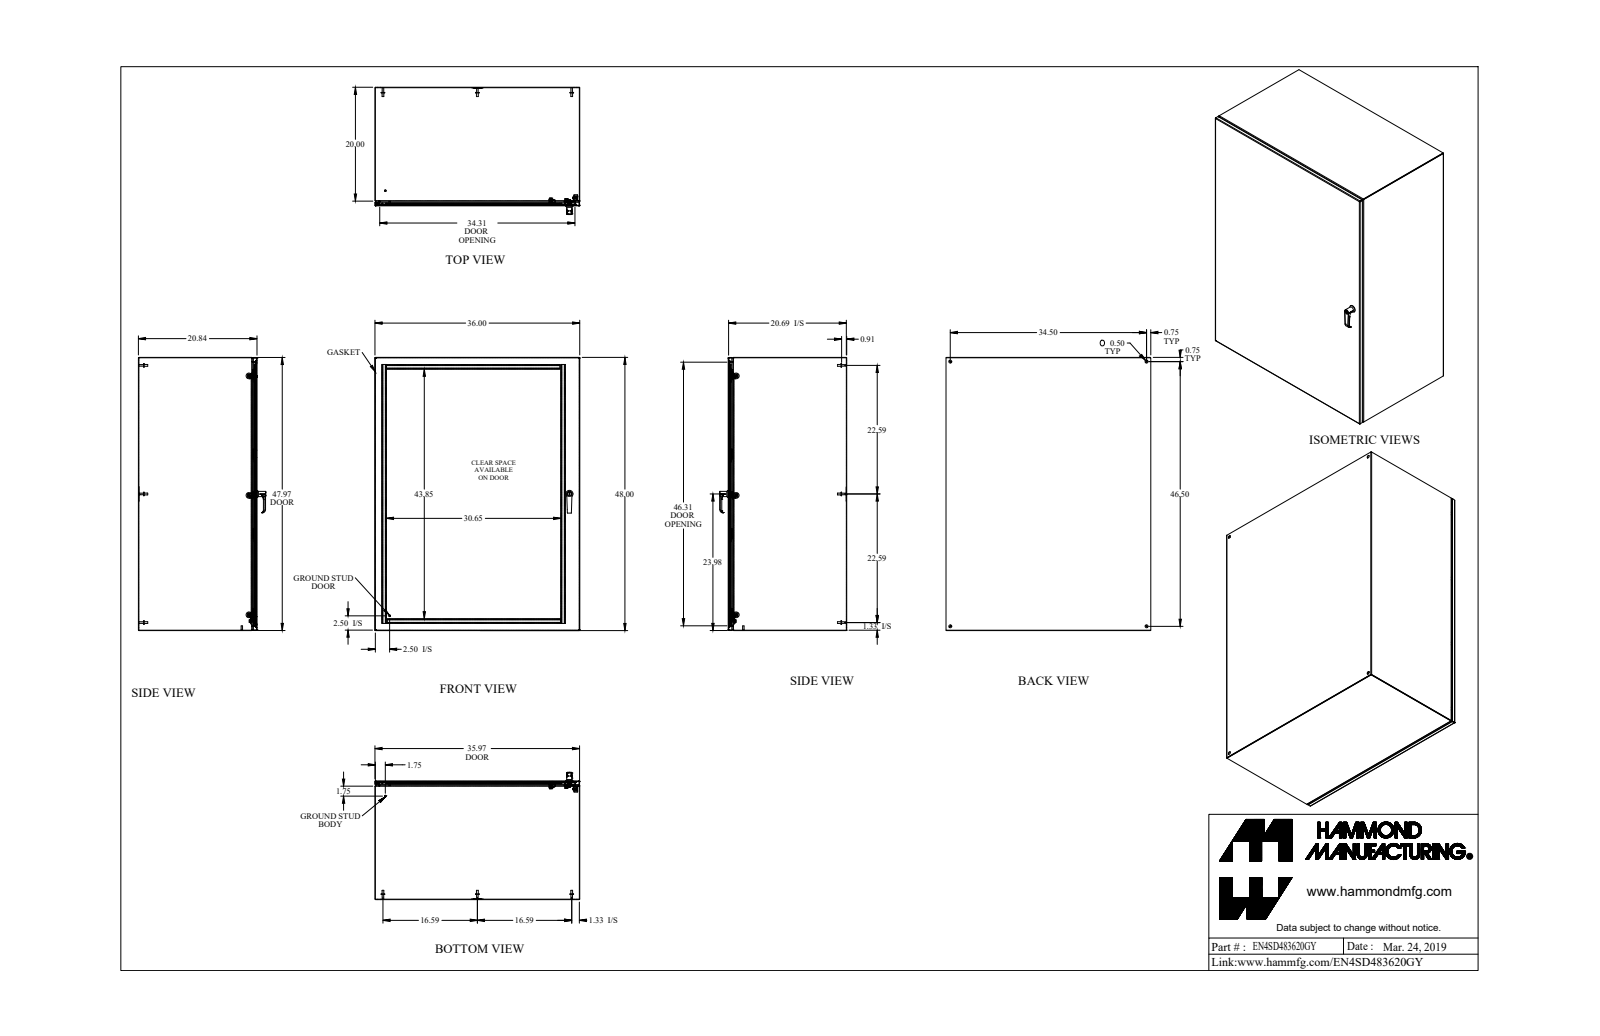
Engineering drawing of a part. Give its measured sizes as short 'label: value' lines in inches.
name: EN4SD483620GY
written by: SolidWorks 2018 (AUTOMOTIVE_DESIGN)
unit: in
bodies: 63 solids, 1719 faces (757 planar, 632 cylindrical, 330 other)
size: 48 × 36 × 22.367
volume: 551.1 in³; area: 15 408 in²
holes: 6× ⌀0.176, 4× ⌀0.196, 4× ⌀0.5, 3× ⌀0.25, 3× ⌀0.265, 3× ⌀0.413, 2× ⌀0.256, 2× ⌀0.313, 2× ⌀0.394, 1× ⌀0.172, 1× ⌀0.24, 1× ⌀0.242
bosses: 8× ⌀0.313, 8× ⌀0.27, 7× ⌀0.25, 6× ⌀0.625, 6× ⌀0.375, 6× ⌀0.156, 3× ⌀1, 3× ⌀0.625
rounds: 24× R0.043, 24× R0.081, 21× R0.062, 18× R0.036, 18× R0.108, 15× R0.03, 10× R0.094, 9× R0.016
face distances: 0.072, 20.765, 35.928, 20.693, 20.837, 35.856, 36, 0.072, 47.856, 47.928
hole spacings: 41.969, 0.787, 20.981, 20.988, 21, 33.504, 34.5, 46.5
